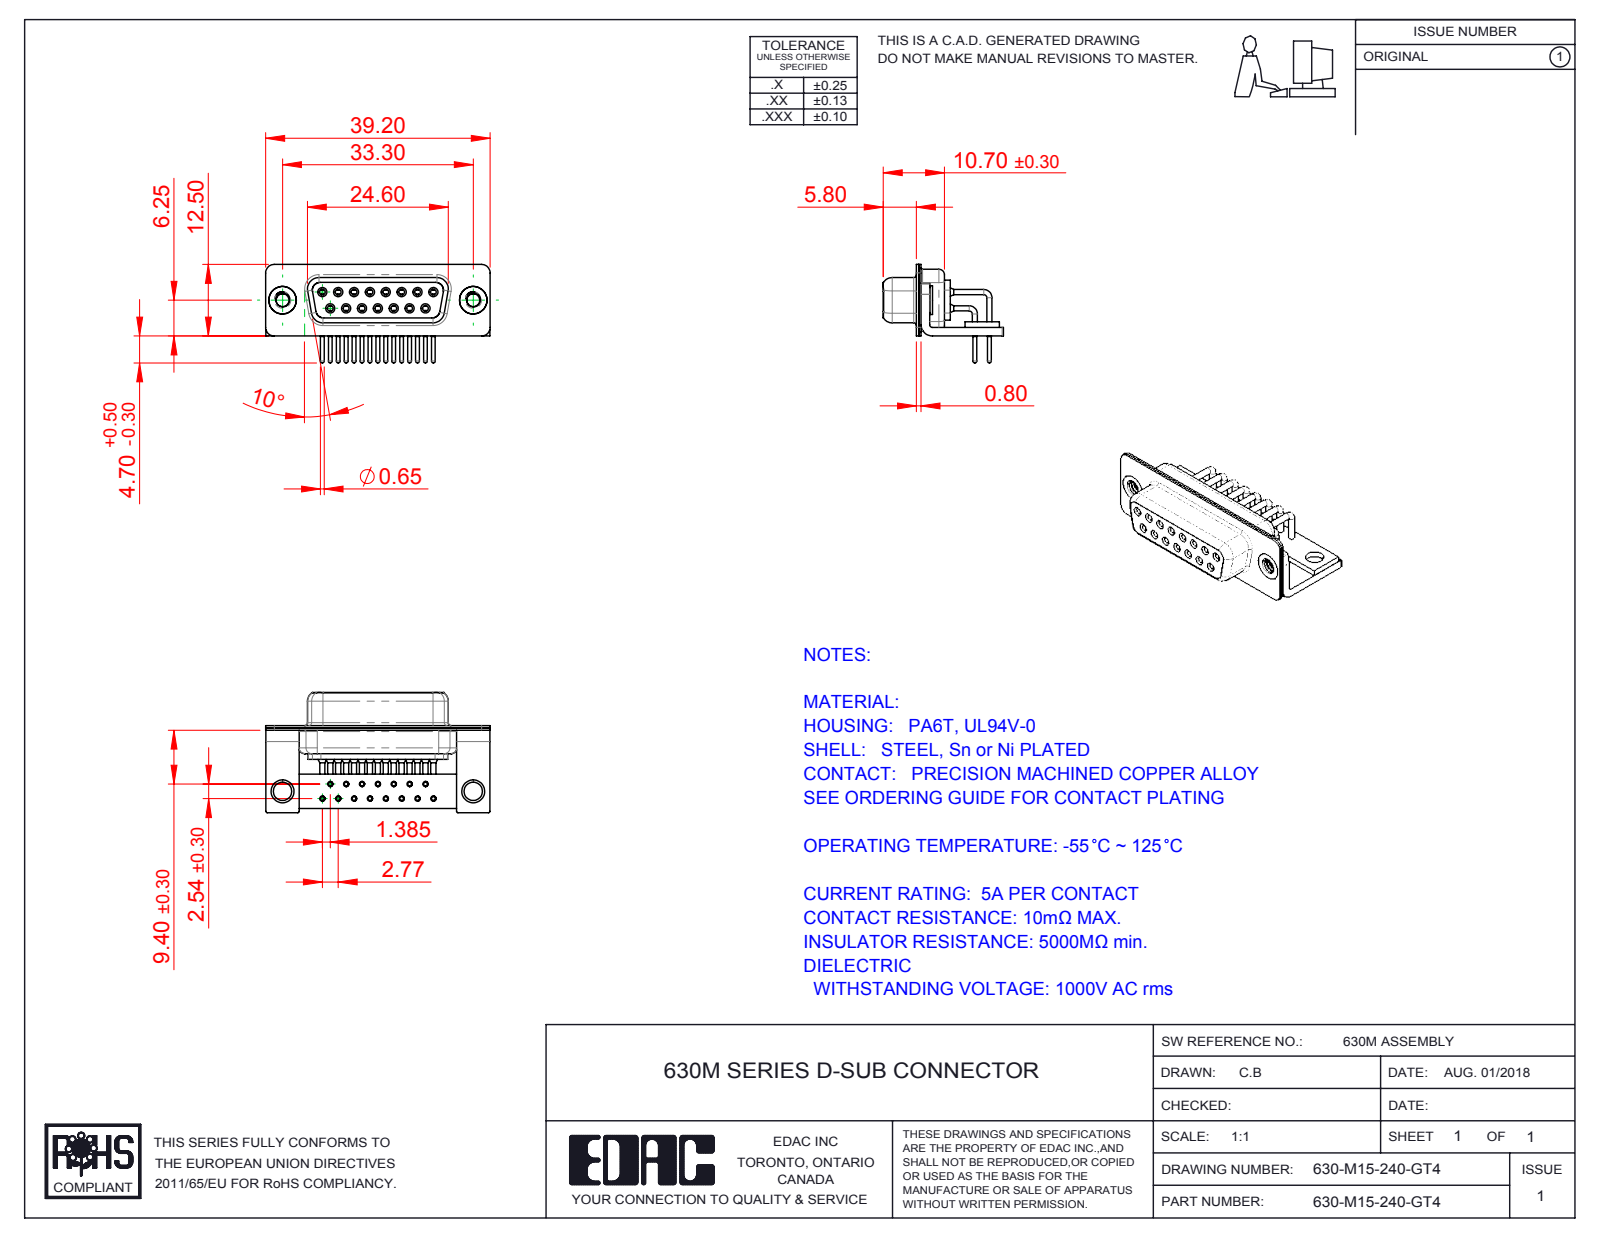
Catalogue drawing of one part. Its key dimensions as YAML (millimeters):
part_name: "630M Housing_15 Contacts; 630M Contact Row 1; 630-M15-240-GT4; 630M 4-40 Threaded Rivet_Stabilizer (+5 more)"
step_written_by: "SolidWorks 2016 (CONFIG_CONTROL_DESIGN)"
units: millimeters
bodies: {solids: 23, faces: 1154, planar: 318, cylindrical: 534, other: 302}
overall_size: [39.2, 21, 17.2]
volume: 3044
surface_area: 7715
round_holes:
  - {diameter: 0.9, count: 15}
  - {diameter: 1, count: 15}
  - {diameter: 1.1, count: 15}
  - {diameter: 1.7, count: 15}
  - {diameter: 1.8, count: 15}
  - {diameter: 2, count: 15}
  - {diameter: 2.26, count: 2}
  - {diameter: 3.2, count: 2}
  - {diameter: 4, count: 2}
  - {diameter: 4.8, count: 2}
round_bosses_or_shafts:
  - {diameter: 0.9, count: 27}
  - {diameter: 1.6, count: 15}
  - {diameter: 1.5, count: 15}
  - {diameter: 0.65, count: 15}
  - {diameter: 5, count: 2}
  - {diameter: 4.9, count: 2}
partial_cylinders:
  - {radius: 0.25, count: 16}
  - {radius: 1.5, count: 16}
  - {radius: 2, count: 13}
  - {radius: 1.35, count: 8}
  - {radius: 1.6, count: 8}
  - {radius: 0.5, count: 5}
  - {radius: 0.6, count: 4}
  - {radius: 0.65, count: 4}
face_to_face_distances: [0.4, 0.8, 2.3, 9.35, 1.9, 1.5, 1, 1.45, 8.95, 0.85]
hole_center_spacings: [2.77, 5.54, 8.31, 3.16, 4.87, 11.08, 2.89, 7.37]
